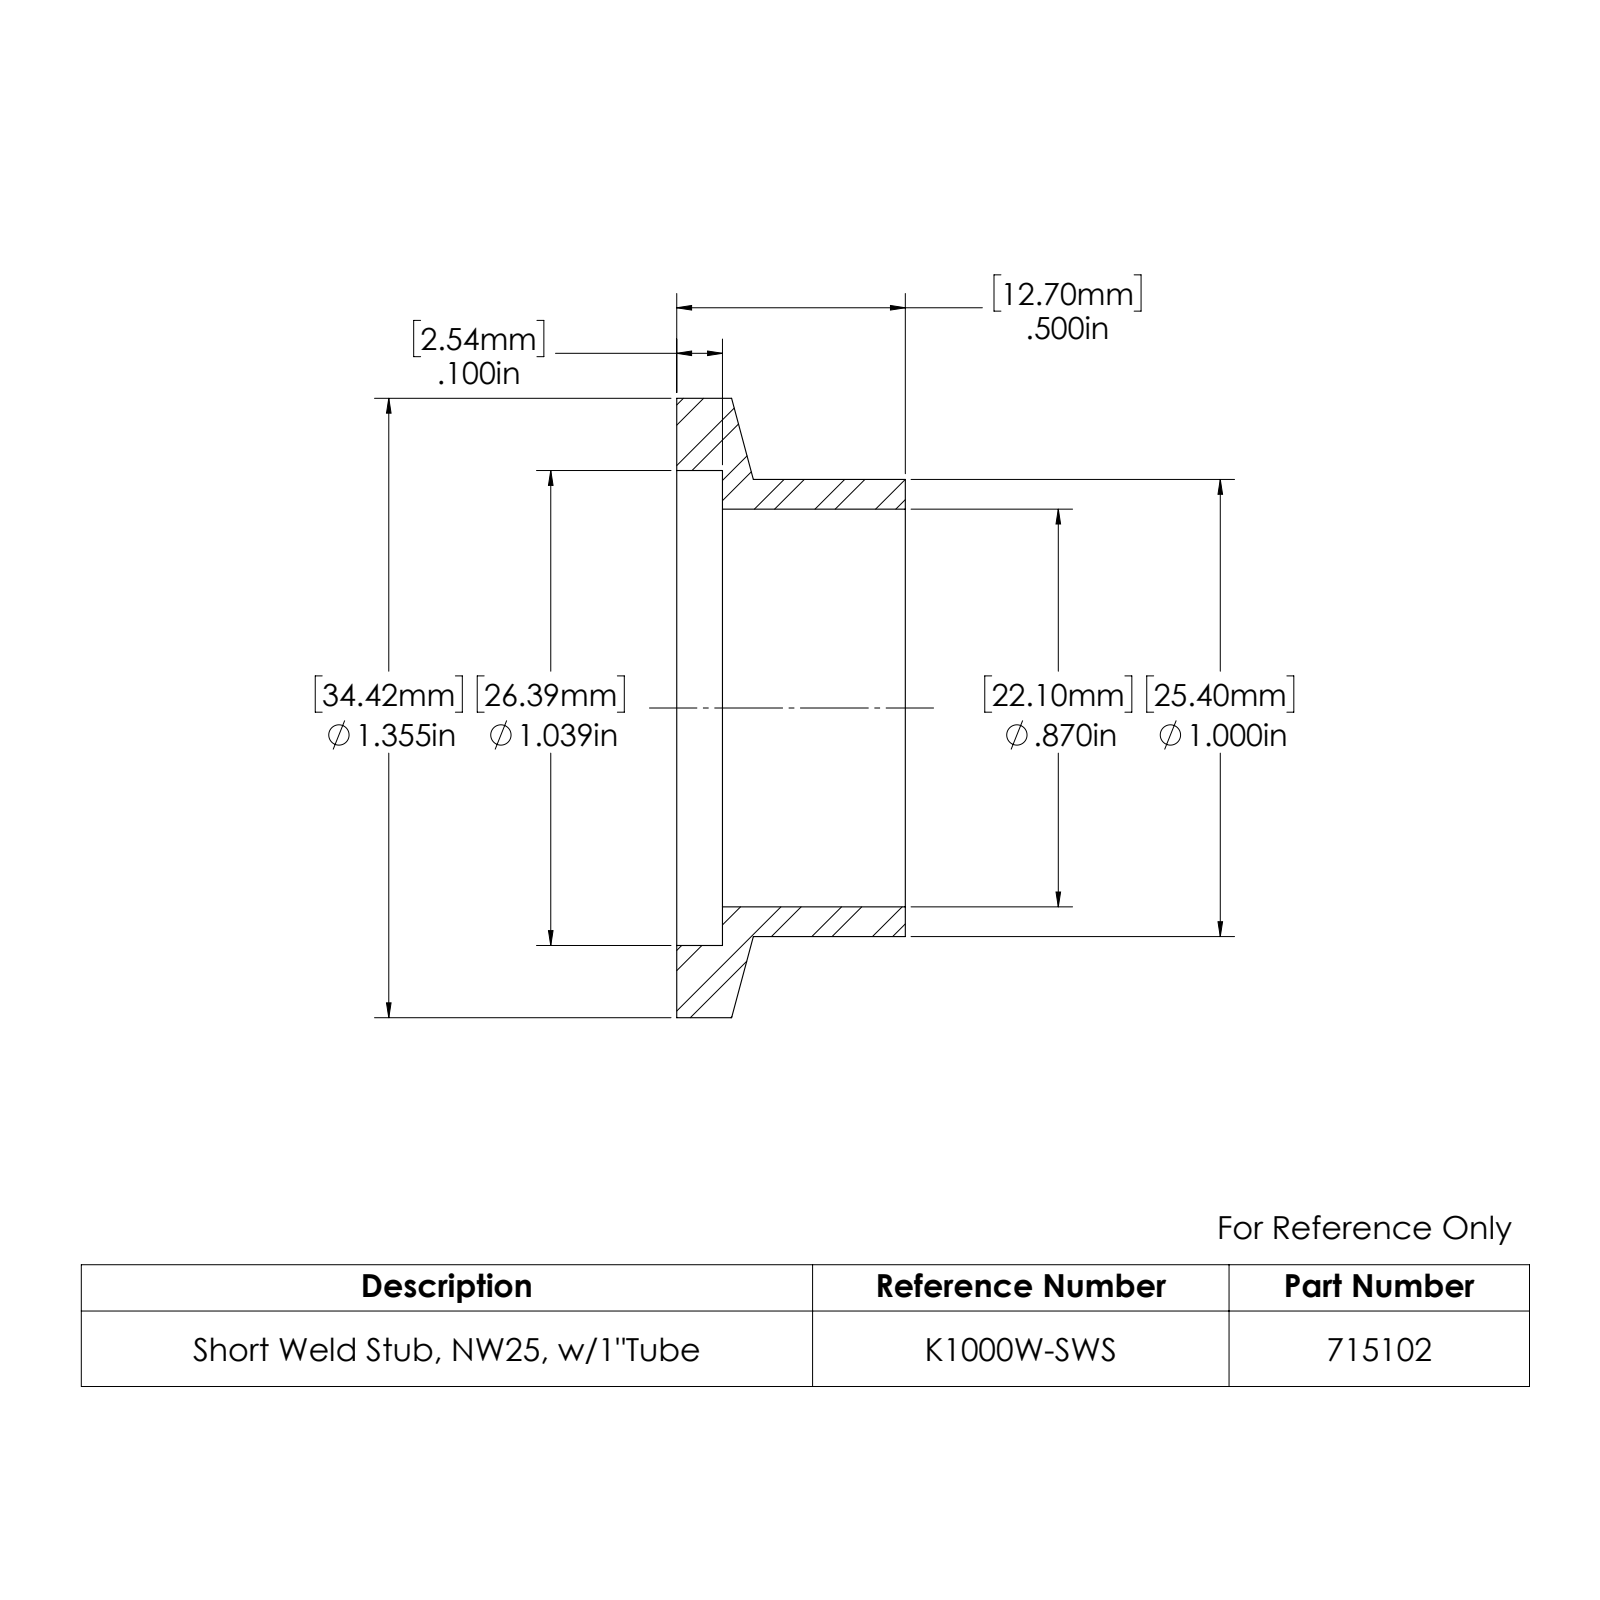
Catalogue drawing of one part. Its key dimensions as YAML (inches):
part_name: "715102"
step_written_by: "SolidWorks 2022 (AUTOMOTIVE_DESIGN)"
units: inches
bodies: {solids: 1, faces: 13, planar: 3, cylindrical: 8, other: 2}
overall_size: [1.355, 1.355, 0.5]
volume: 0.164
surface_area: 4.693
round_holes:
  - {diameter: 0.87, count: 1}
  - {diameter: 1.039, count: 1}
round_bosses_or_shafts:
  - {diameter: 1.355, count: 1}
  - {diameter: 1, count: 1}
face_to_face_distances: [0.1, 0.5, 0.4]
